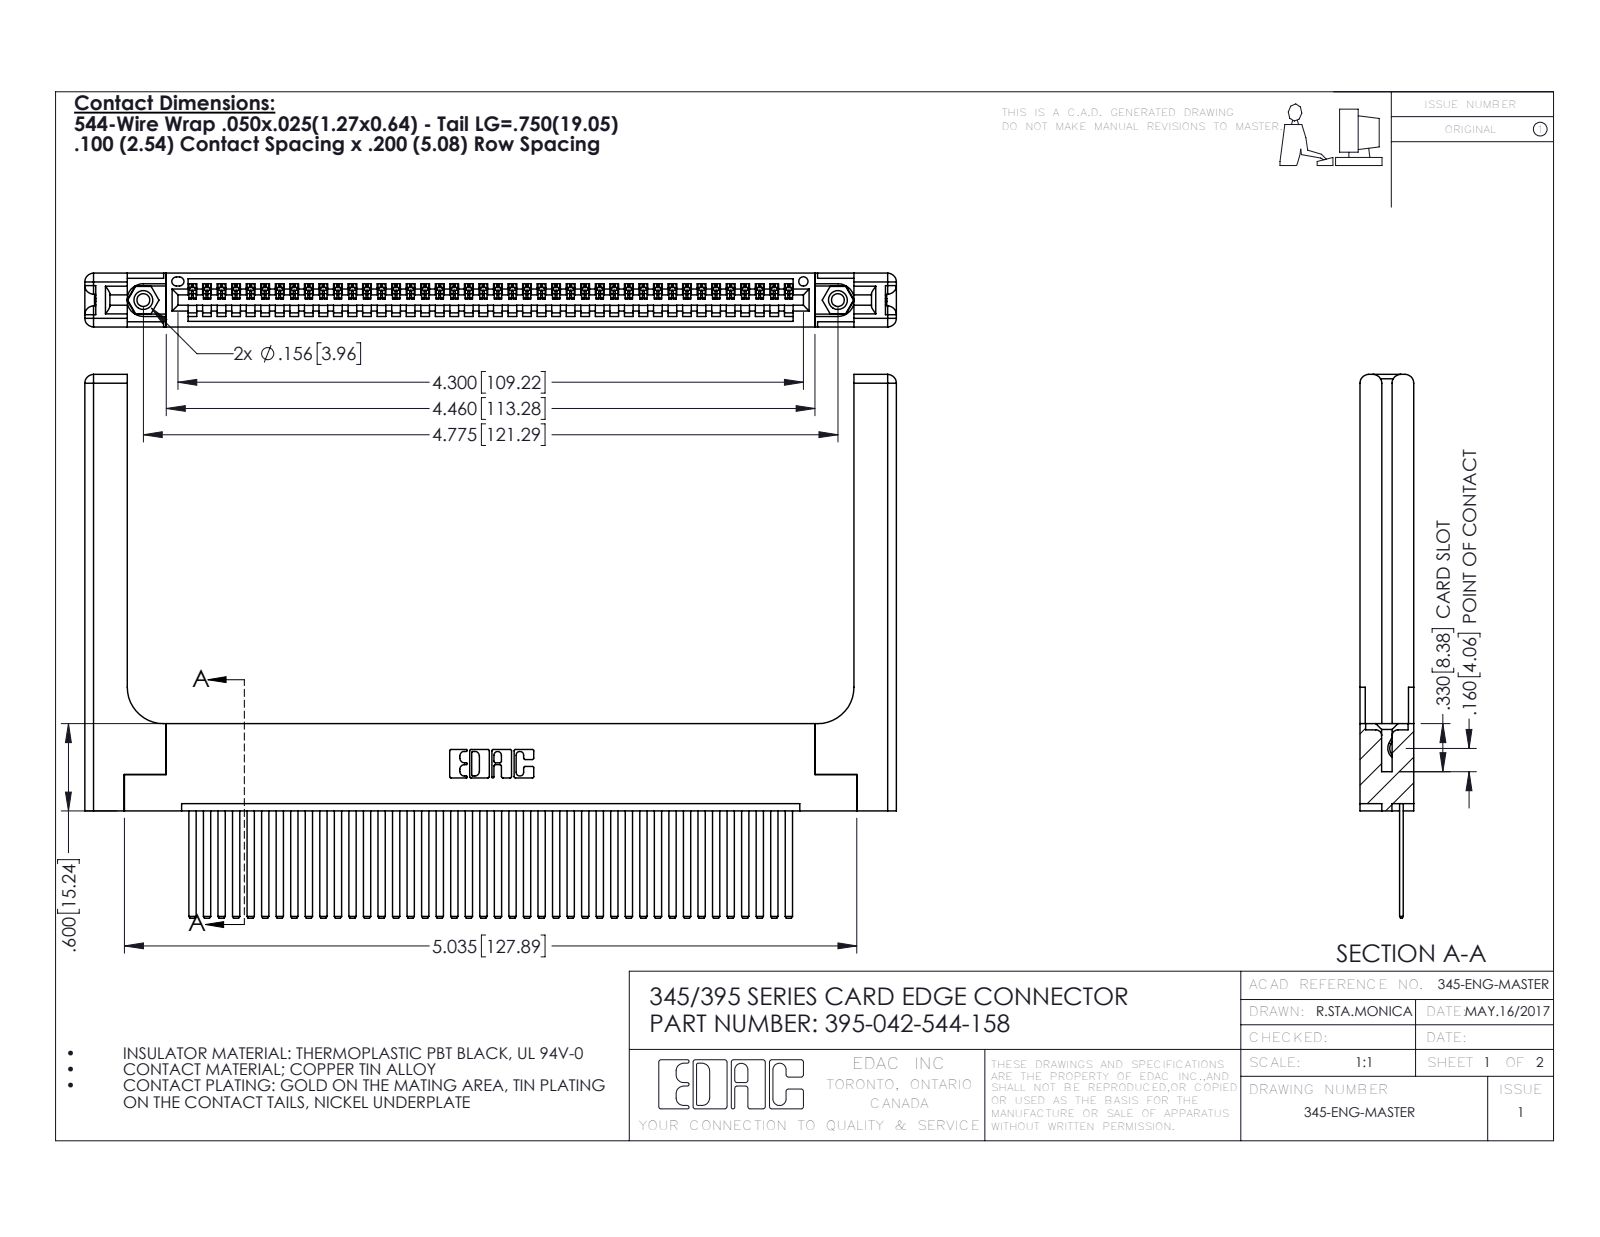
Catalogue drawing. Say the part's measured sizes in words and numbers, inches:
The part is named "395-042-544-158; 345-220-058_345-220-058; 345-250-001_345-250-001-102; 345 Part_Flush Mounting Lugs - 0.156 Dia-TH (+1 more)". Its 3-D file was written by "SolidWorks 2016 (CONFIG_CONTROL_DESIGN)". It is 47 solids with 2566 faces: 1740 planar, 766 cylindrical and 60 other. Overall it measures 5.579 by 3.737 by 0.37 inches. Its volume is 1.37 cubic inches and its surface area 39.21 square inches. Round holes: 2 of diameter 0.089, 2 of diameter 0.125, 2 of diameter 0.156, 1 of diameter 0.064. Round bosses or shafts: 2 of diameter 0.155. Partial cylindrical surfaces (rounded edges, fillets, slot ends): 84 of radius 0.006, 22 of radius 0.01, 16 of radius 0.06, 6 of radius 0.007, 6 of radius 0.031, 3 of radius 0.026, 2 of radius 0.03, 2 of radius 0.031. The main face-to-face distances are 0.072, 0.298, 0.37, 0.098, 0.272, 0.025, 0.2, 0.148, 0.15, 0.225. The hole center spacings are 0.27, 4.539, 4.775.
